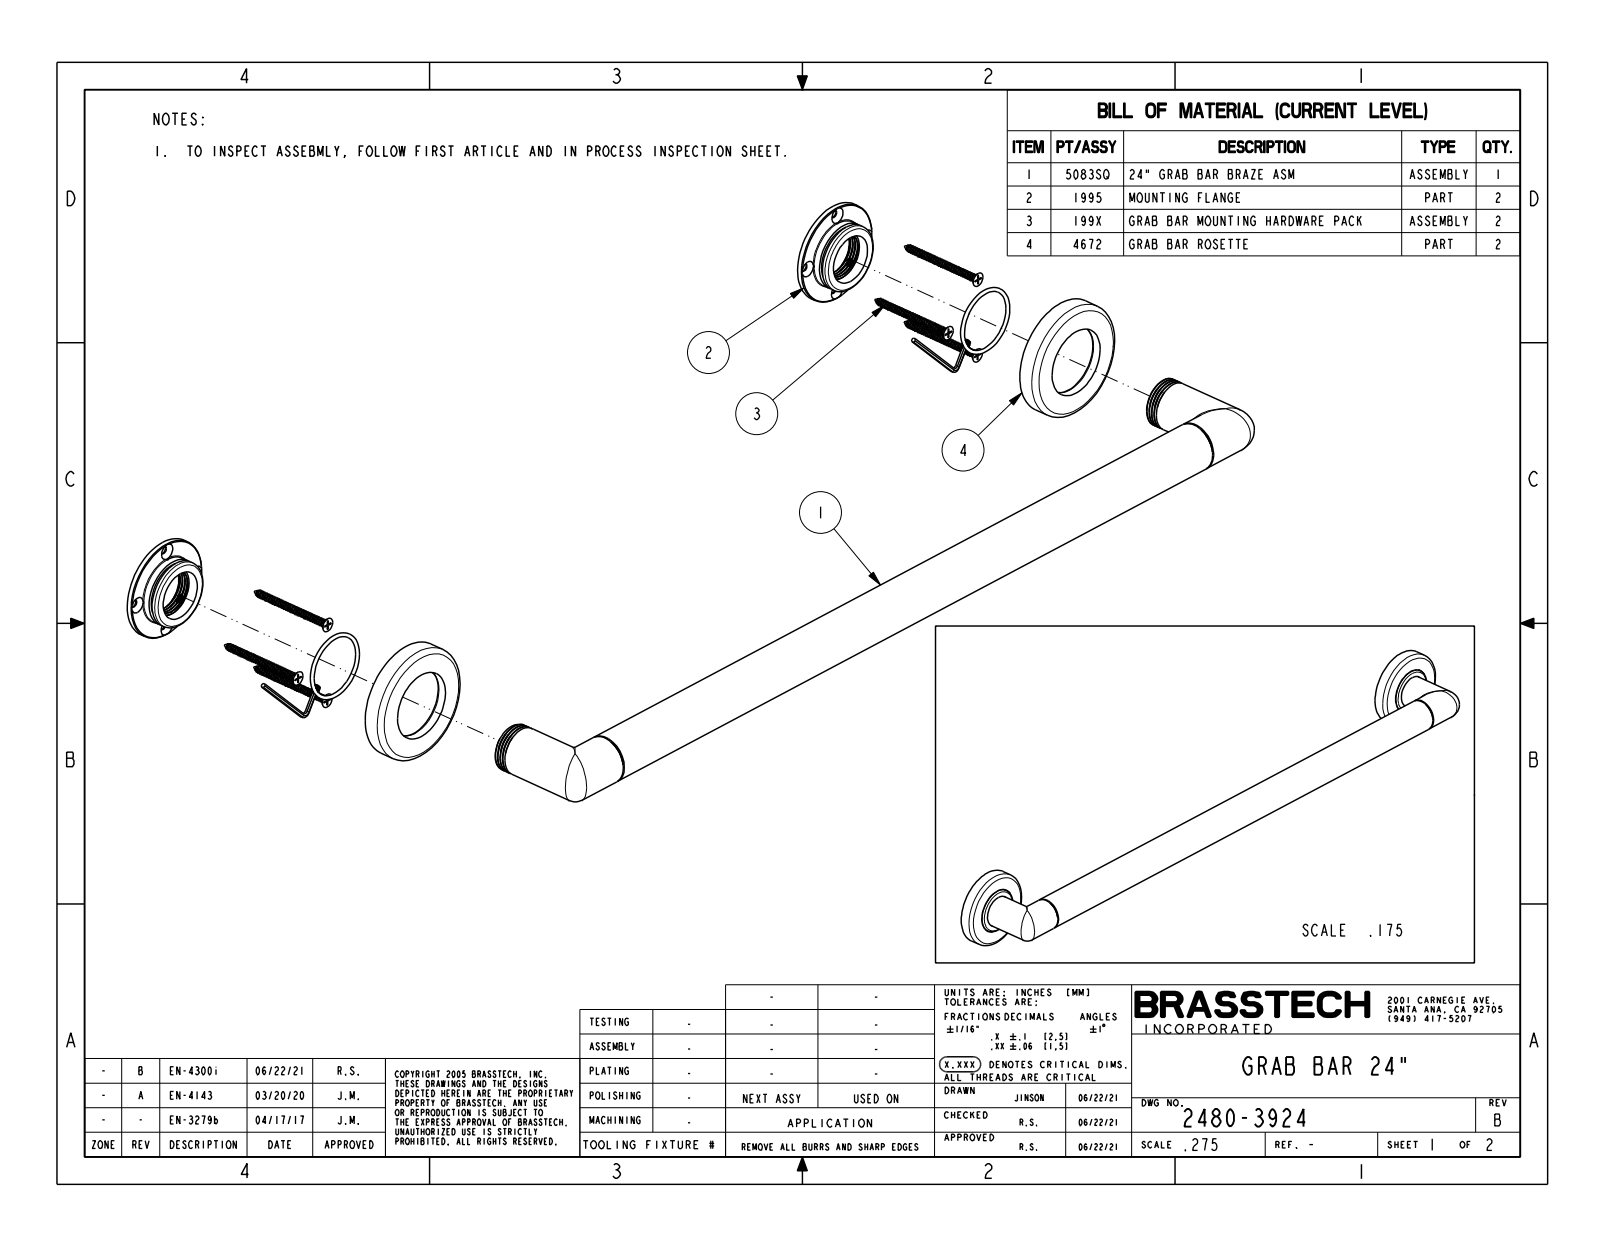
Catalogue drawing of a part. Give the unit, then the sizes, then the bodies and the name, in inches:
Units: inches
Overall size (bounding box): 27 × 3 × 2.755
Round bosses / shafts (diameter × count): ⌀1.25 ×3, ⌀3 ×2, ⌀1.75 ×2
Main face-to-face distances: 0.53, 0.6, 0.07
Volume: 40.92 in³ · Surface area: 141.3 in²
Bodies: 1 solid, 48 faces (6 planar, 18 cylindrical, 24 other)
Part name (STEP PRODUCT): 2480-3924
STEP written by: CREO PARAMETRIC BY PTC INC, 2018400 (CONFIG_CONTROL_DESIGN)
